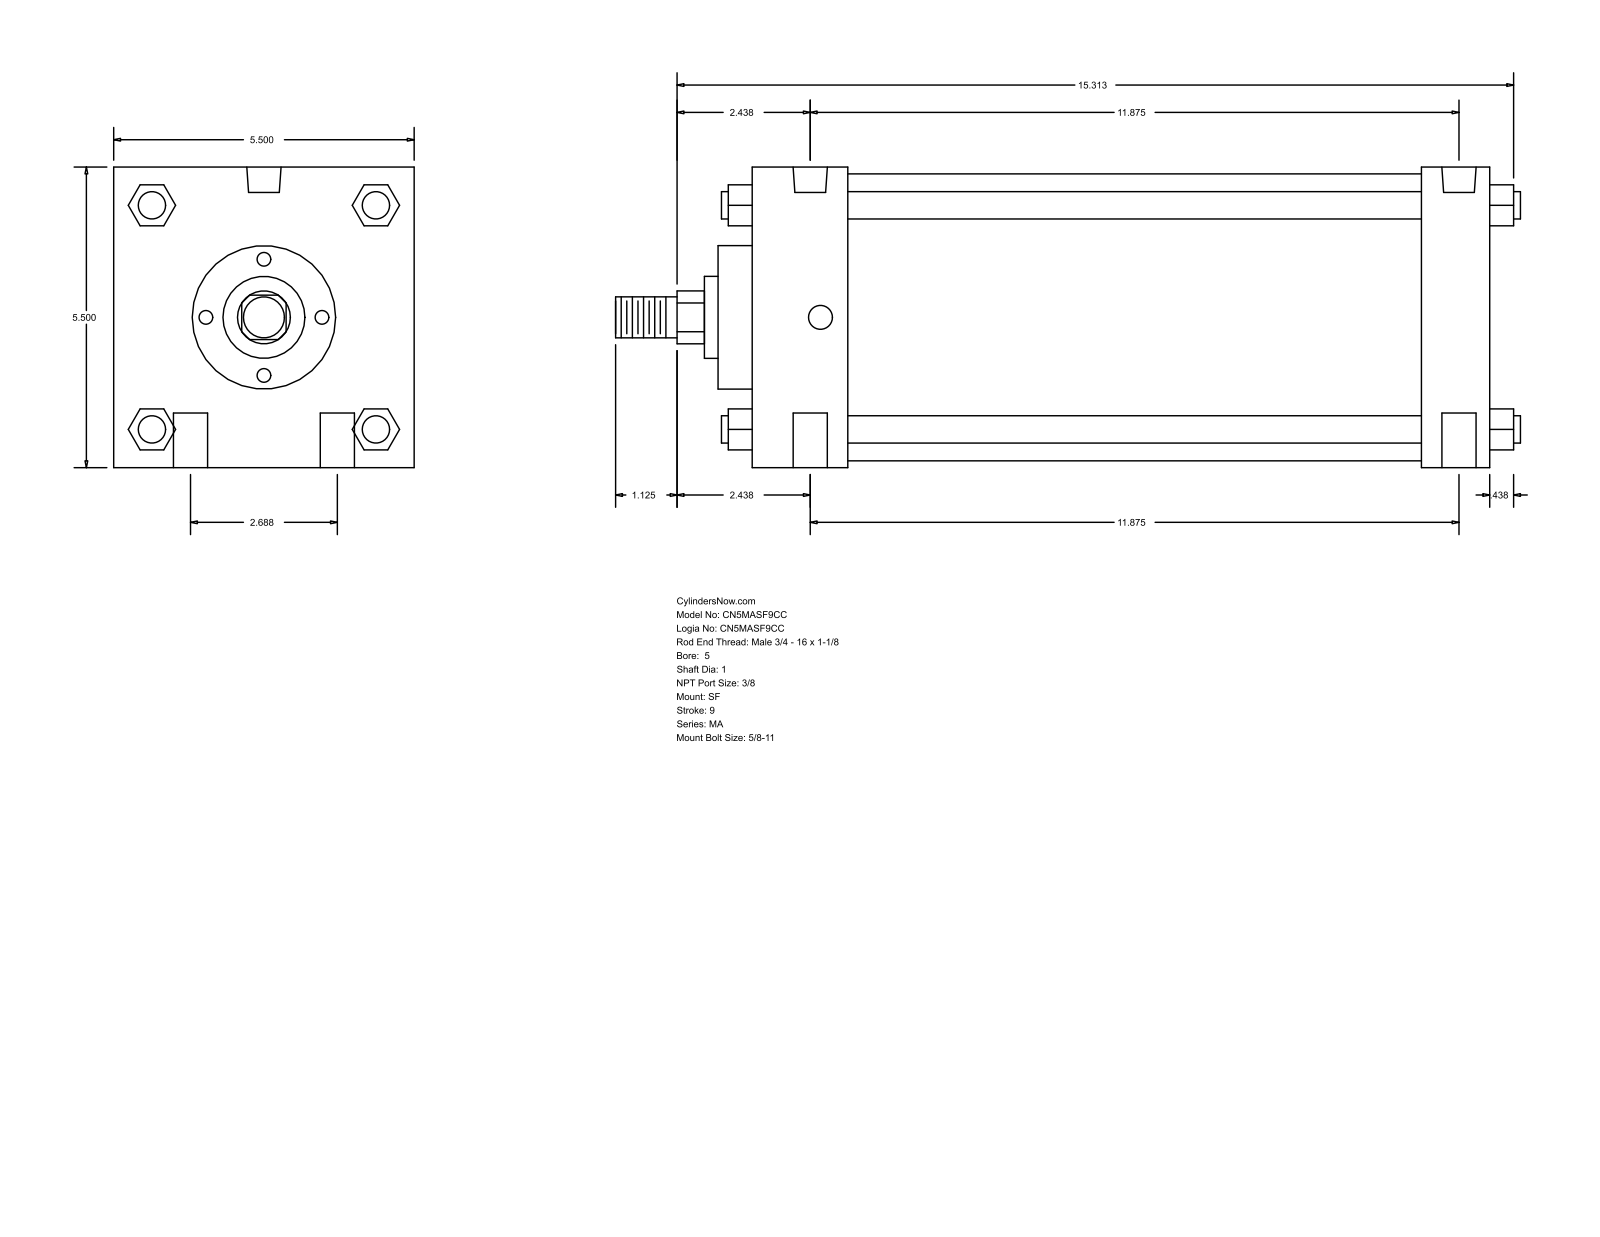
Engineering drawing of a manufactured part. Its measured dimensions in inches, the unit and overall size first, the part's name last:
Units: inches
Overall size (bounding box): 16.563 × 5.5 × 5.5
Round holes (diameter × count): ⌀0.625 ×4, ⌀0.437 ×2, ⌀0.627 ×2
Round bosses / shafts (diameter × count): ⌀0.5 ×4, ⌀5.25 ×1, ⌀2.625 ×1, ⌀1.5 ×1, ⌀1 ×1, ⌀0.75 ×1
Partial cylindrical surfaces — rounded edges, fillets, slot ends (radius × count): R0.484 ×1
Main face-to-face distances: 5.5, 13.5, 1.75, 12.25, 10.5, 11.75, 1.25, 0.625, 2.375, 12.875
Hole centre spacings: 1.344, 11.951, 11.875, 2.687, 12.176, 11.5
Bodies: 0 solids, 126 faces (95 planar, 31 cylindrical, 0 other)
Part name (STEP PRODUCT): MA_SF__0500_1
STEP written by: GSSL Pune (CONFIG_CONTROL_DESIGN)
